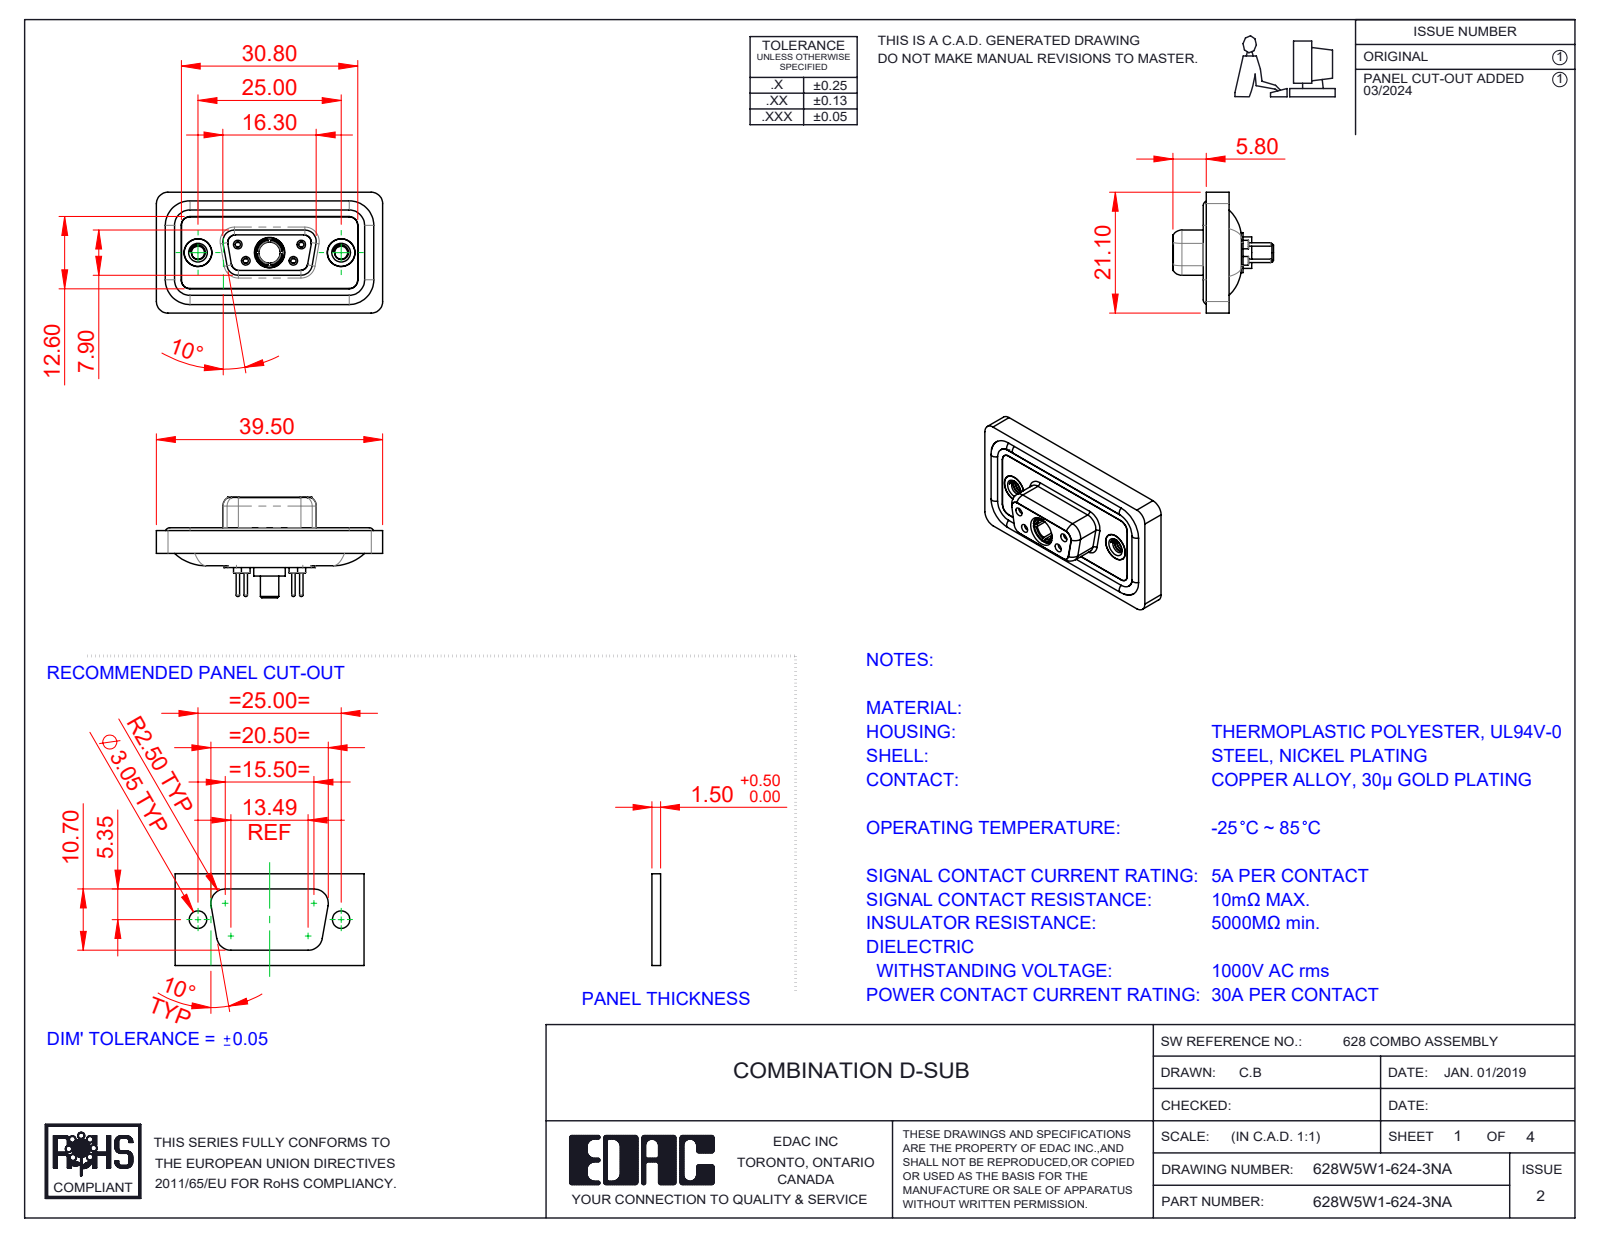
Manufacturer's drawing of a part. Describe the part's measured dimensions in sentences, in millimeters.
The part is named "628Combo Threaded Rivet_A; 628Combo Contact Row 1_24; 628Combo Waterproof Housing_09 Contacts; 628Combo Shell Front_09 Contacts (+5 more)". Its 3-D file was written by "SolidWorks 2023 (CONFIG_CONTROL_DESIGN)". It is 13 solids with 678 faces: 194 planar, 289 cylindrical and 195 other. Overall it measures 39.5 by 21.1 by 17.55 millimeters. Its volume is 4 776 cubic millimeters and its surface area 7 637 square millimeters. Round holes: 4 of diameter 0.9, 4 of diameter 1.1, 4 of diameter 1.5, 4 of diameter 2, 3 of diameter 4.85, 2 of diameter 1.6, 2 of diameter 1.7, 2 of diameter 2.26, 2 of diameter 4, 2 of diameter 4.05, 2 of diameter 5, 1 of diameter 3.7. Round bosses or shafts: 6 of diameter 1.6, 4 of diameter 2.2, 4 of diameter 0.6, 2 of diameter 4.95, 2 of diameter 4.8, 1 of diameter 5.5, 1 of diameter 5.2, 1 of diameter 4.96. Partial cylindrical surfaces (rounded edges, fillets, slot ends): 22 of radius 1.5, 18 of radius 2, 8 of radius 1.35, 8 of radius 1.6, 4 of radius 0.25, 4 of radius 0.5, 4 of radius 0.6, 4 of radius 0.65. The main face-to-face distances are 0.4, 2.9, 1.1, 1.8, 1.6, 0.5, 5.65, 7.45, 5.35, 3.6. The hole center spacings are 3.16, 5.72, 7.1, 12.5, 18.1, 4.39, 4.4, 8.31.
